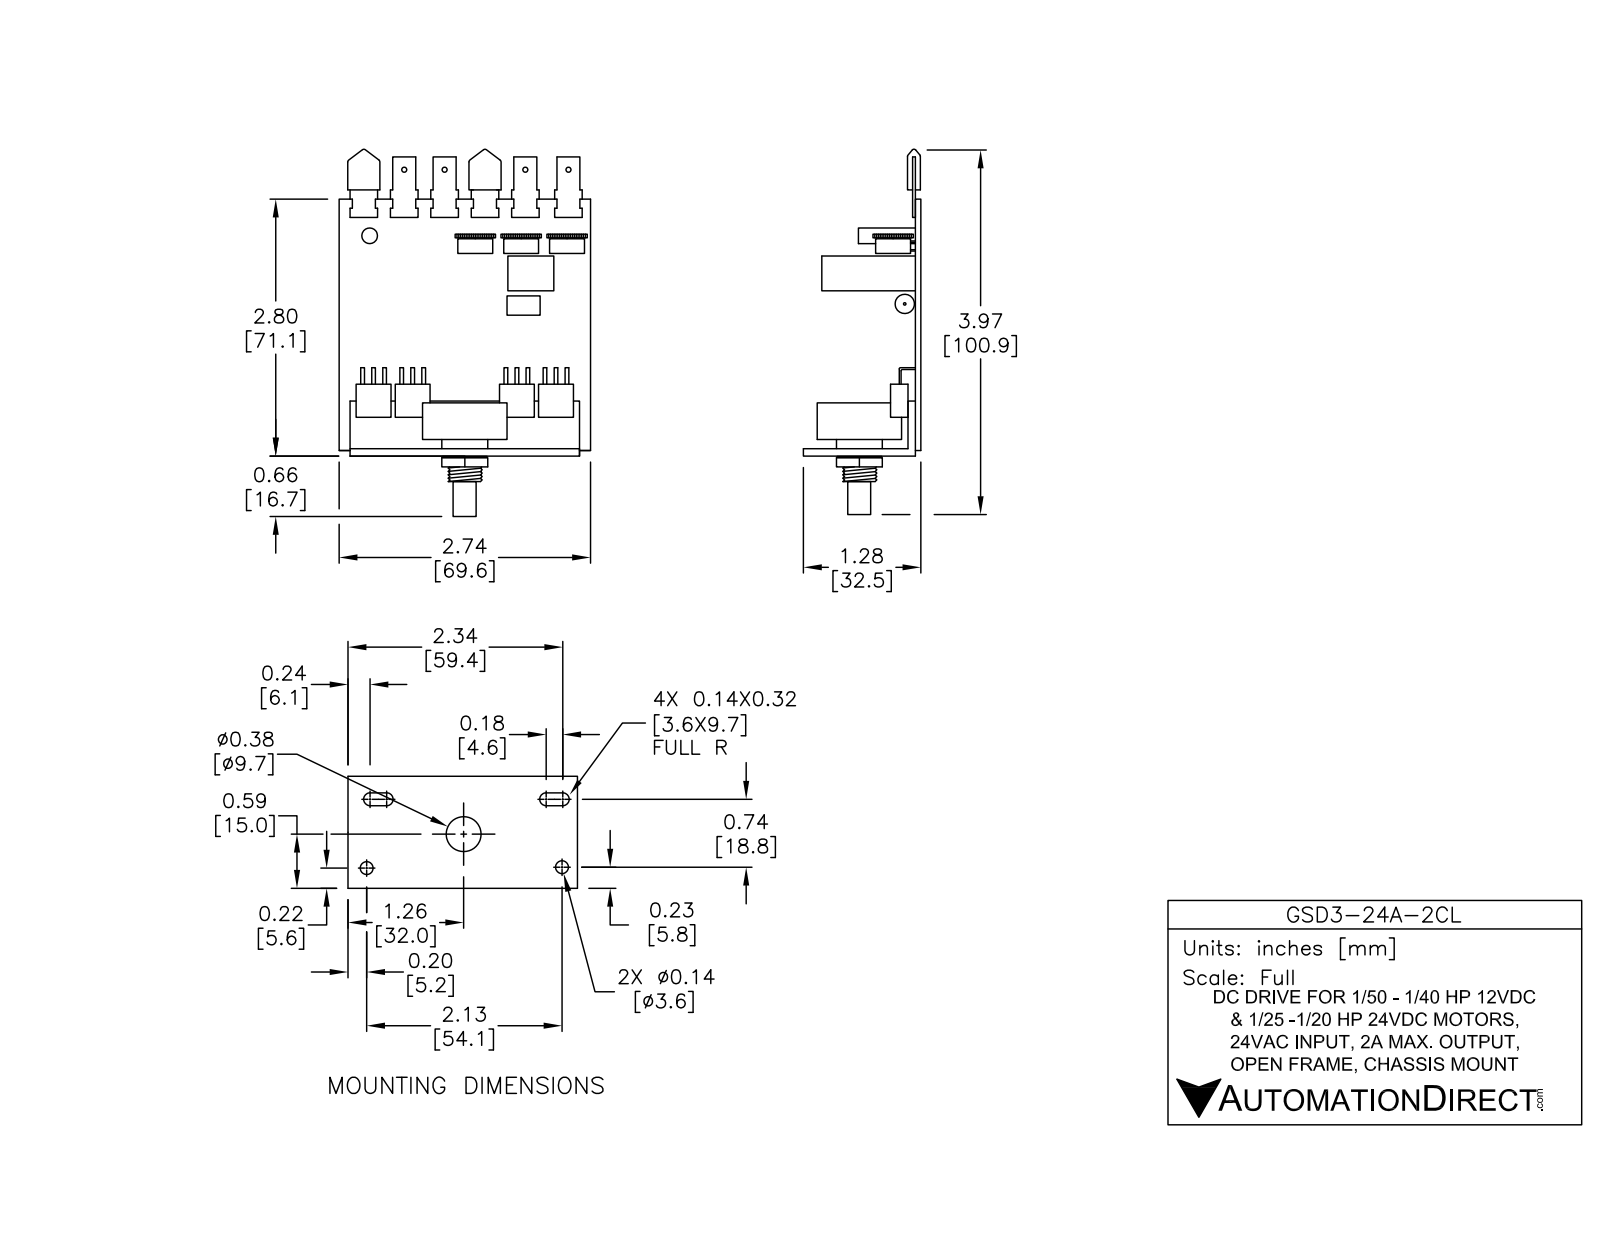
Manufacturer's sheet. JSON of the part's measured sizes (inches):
{"part_name": "Speedpot_Lockwasher; DIOM_SMA; CP4910; CAP_3216_TANT (+8 more)", "step_written_by": "SolidWorks 2014 (AUTOMOTIVE_DESIGN)", "units": "inches", "bodies": {"solids": 107, "faces": 3277, "planar": 2062, "cylindrical": 1023, "other": 192}, "overall_size": [3.845, 2.734, 1.368], "volume_in3": 1.804, "surface_area_in2": 48.86, "round_holes": [[0.026, 22], [0.052, 18], [0.033, 15], [0.043, 14], [0.046, 14], [0.067, 11], [0.14, 7], [0.04, 6], [0.08, 4], [0.11, 4], [0.144, 4], [0.048, 3]], "round_bosses_or_shafts": [[0.022, 8], [0.026, 6], [0.025, 6], [0.25, 5], [0.156, 4], [0.354, 3], [0.106, 3], [0.051, 3]], "partial_cylinders_radius": [[0.004, 48], [0.025, 21], [0.05, 12], [0.02, 8], [0.039, 4], [0.07, 4], [0.091, 4], [0.225, 3]], "face_to_face_distances": [0.063, 0.08, 0.143, 0.035, 0.098, 0.045, 0.263, 0.5, 0.326, 0.496], "hole_center_spacings": [0.15, 0.3, 0.369, 0.451, 0.58, 0.151, 0.233, 0.276]}
